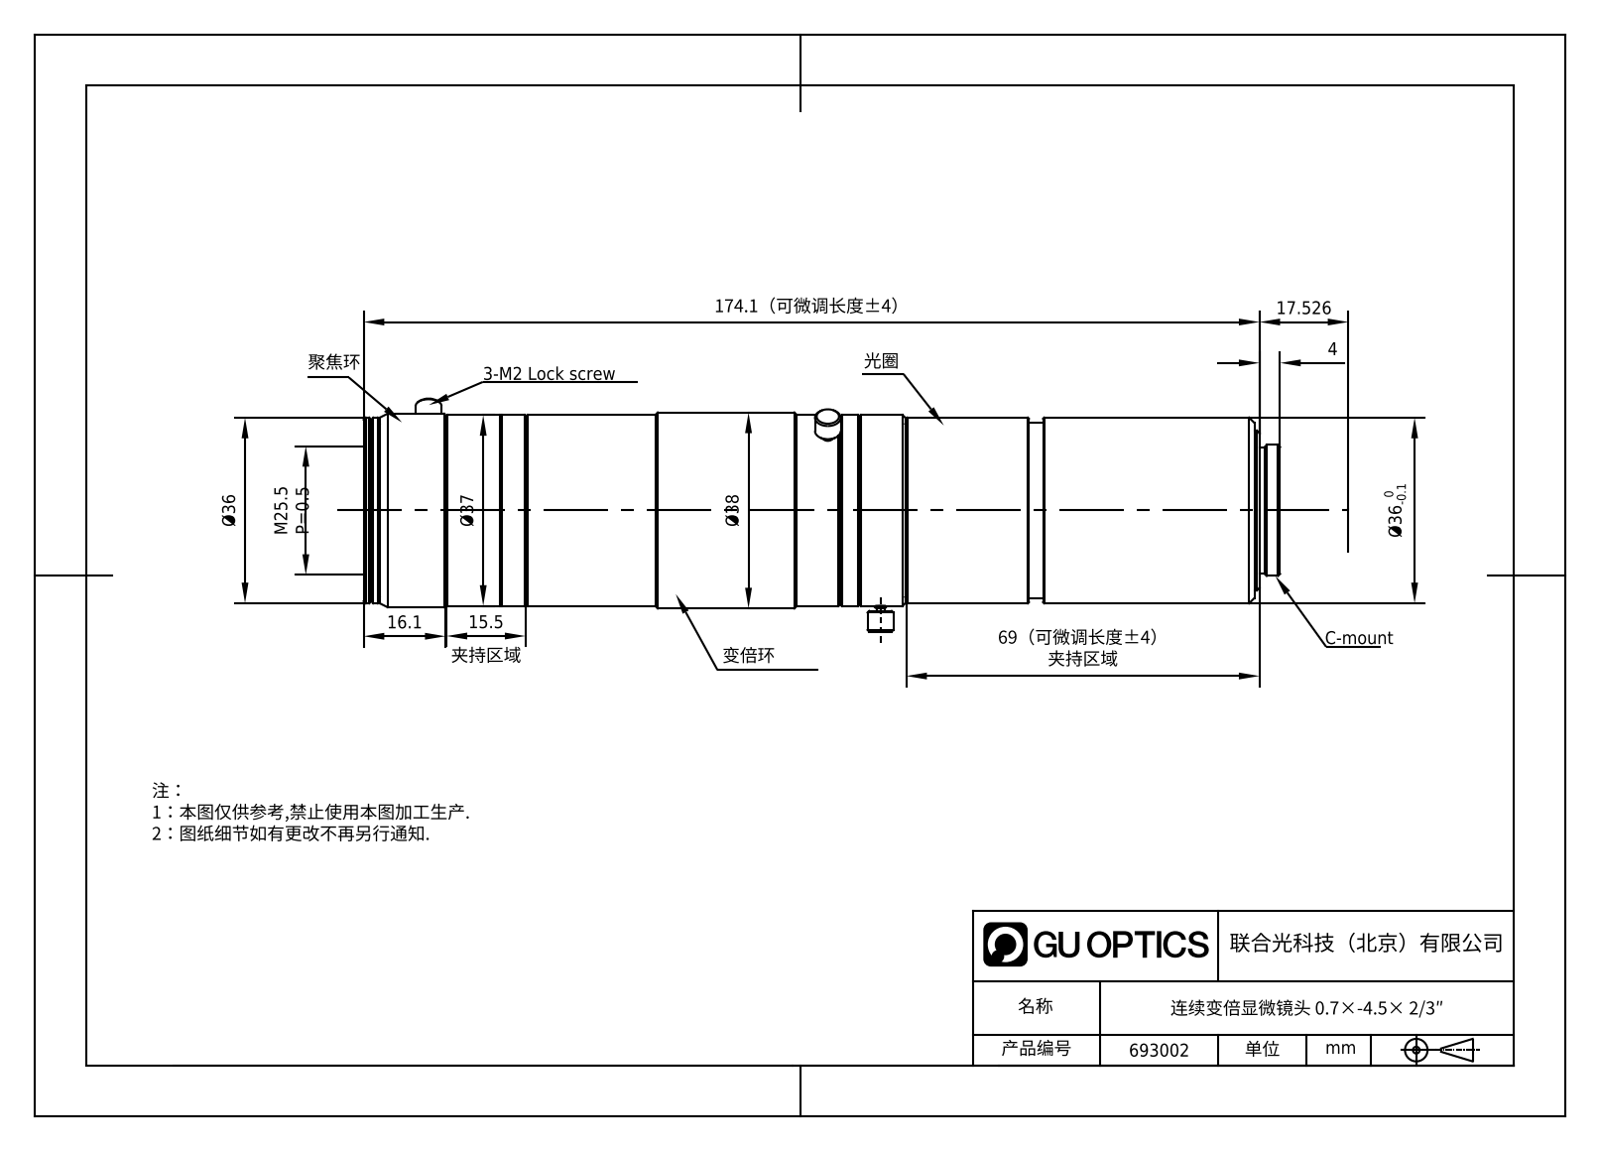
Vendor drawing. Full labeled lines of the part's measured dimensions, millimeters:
Part name (STEP PRODUCT): VSZ-0745
STEP written by: SolidWorks 2012 (CONFIG_CONTROL_DESIGN)
Units: millimetres
Bodies: 1 solid, 229 faces (35 planar, 78 cylindrical, 116 other)
Overall size (bounding box): 177.85 × 45.2 × 38
Volume: 150 278 mm³ · Surface area: 32 525 mm²
Round holes (diameter × count): ⌀9 ×1, ⌀20 ×1, ⌀22 ×1, ⌀24 ×1, ⌀24.5 ×1, ⌀25 ×1, ⌀25.5 ×1, ⌀27.5 ×1, ⌀28 ×1, ⌀32.5 ×1, ⌀33.5 ×1, ⌀34 ×1
Round bosses / shafts (diameter × count): ⌀5 ×3, ⌀2 ×3, ⌀1.6 ×3, ⌀38 ×1, ⌀37.5 ×1, ⌀37 ×1, ⌀36 ×1, ⌀33.9 ×1
Main face-to-face distances: 13, 93.2, 93, 171.64, 106.9, 64.74, 12.8, 127.5, 34.5, 127.7
